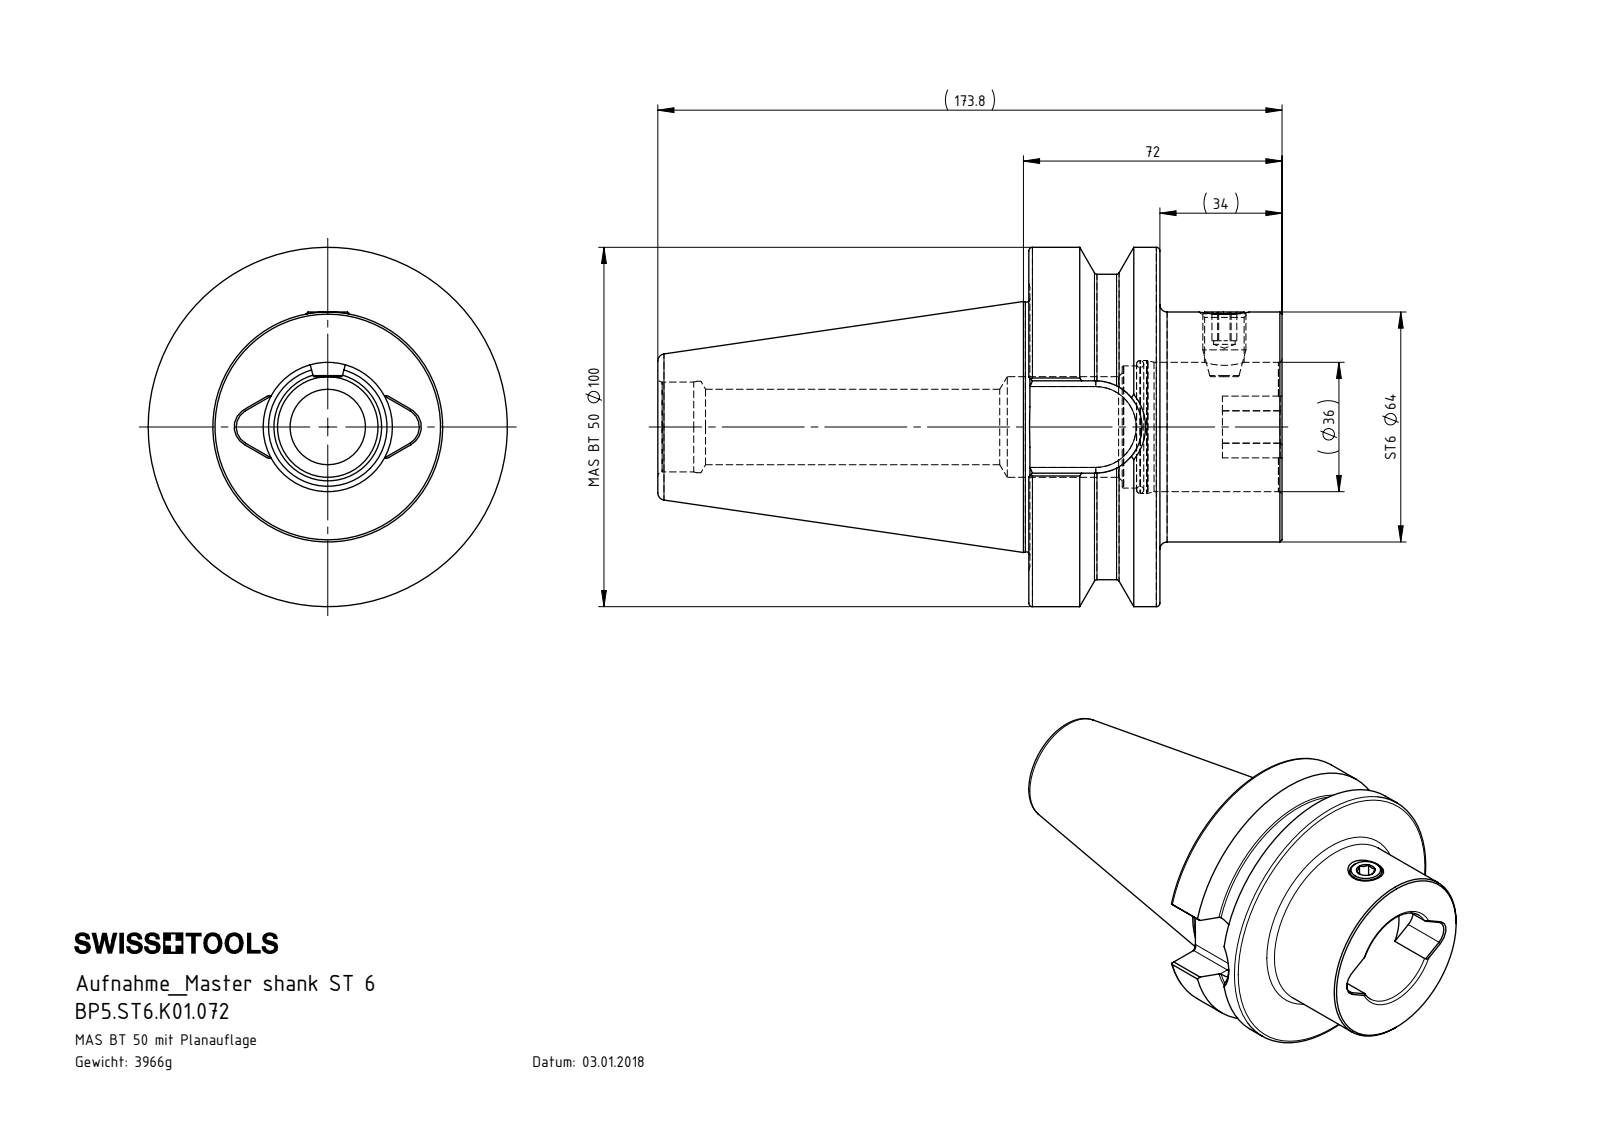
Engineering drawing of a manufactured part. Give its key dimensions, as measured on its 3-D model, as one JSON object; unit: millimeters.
{"part_name": "ST6-ER1.001.018_A; BP5.ST6.K01.072; BP5-ST6.K01.072_A; DIN 3771 - 33x2", "step_written_by": "SolidWorks 2017 (AUTOMOTIVE_DESIGN)", "units": "millimeters", "bodies": {"solids": 3, "faces": 163, "planar": 45, "cylindrical": 42, "other": 76}, "overall_size": [173.8, 100, 100], "volume_mm3": 505583, "surface_area_mm2": 67042, "round_holes": [[6, 1], [11, 1], [21, 1], [25, 1], [25.45, 1], [28, 1], [34, 1], [36, 1], [37, 1]], "round_bosses_or_shafts": [[100, 1], [85, 1], [64, 1], [12, 1]], "partial_cylinders_radius": [[1.6, 8], [5.2, 2], [12.85, 1]], "face_to_face_distances": [36.5, 70.5, 34, 70.6, 36.2, 70.2, 25.7, 103.3, 103.6, 139.8]}
